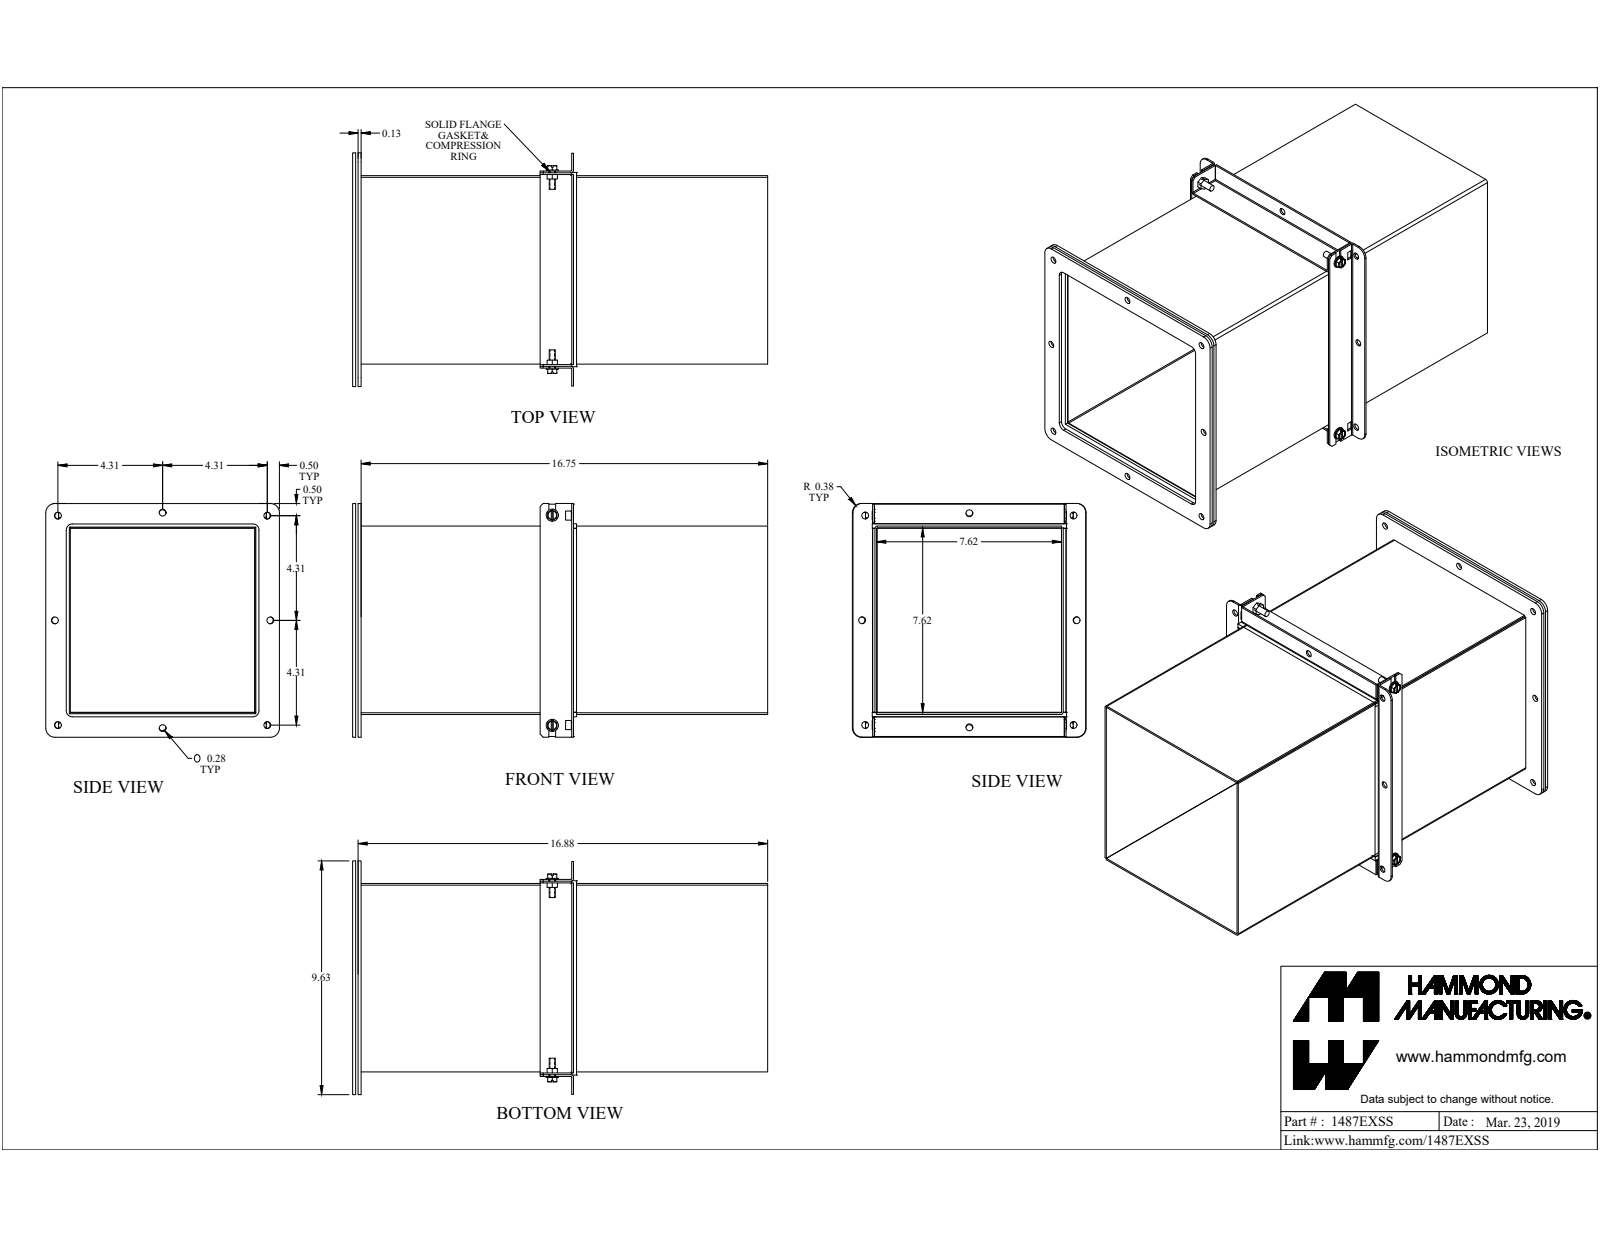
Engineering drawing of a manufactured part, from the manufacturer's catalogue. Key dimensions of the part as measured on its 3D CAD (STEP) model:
Part name (STEP PRODUCT): 1487EXSS
STEP written by: SolidWorks 2019 (CONFIG_CONTROL_DESIGN)
Units: inches
Bodies: 23 solids, 483 faces (309 planar, 134 cylindrical, 40 other)
Overall size (bounding box): 17.446 × 9.629 × 9.625
Volume: 54.78 in³ · Surface area: 1 403 in²
Round holes (diameter × count): ⌀0.281 ×18, ⌀0.196 ×3, ⌀0.35 ×3, ⌀0.258 ×1
Round bosses / shafts (diameter × count): ⌀0.5 ×3, ⌀0.25 ×3
Partial cylindrical surfaces — rounded edges, fillets, slot ends (radius × count): R0.02 ×26, R0.036 ×10, R0.108 ×10, R0.375 ×8, R0.25 ×4
Main face-to-face distances: 0.072, 0.072, 7.688, 7.616, 7.688, 7.76, 7.854, 7.782, 0.125, 0.125
Hole centre spacings: 4.315, 9.755, 9.72, 4.294, 6.276, 8.625, 0.015, 0.026
